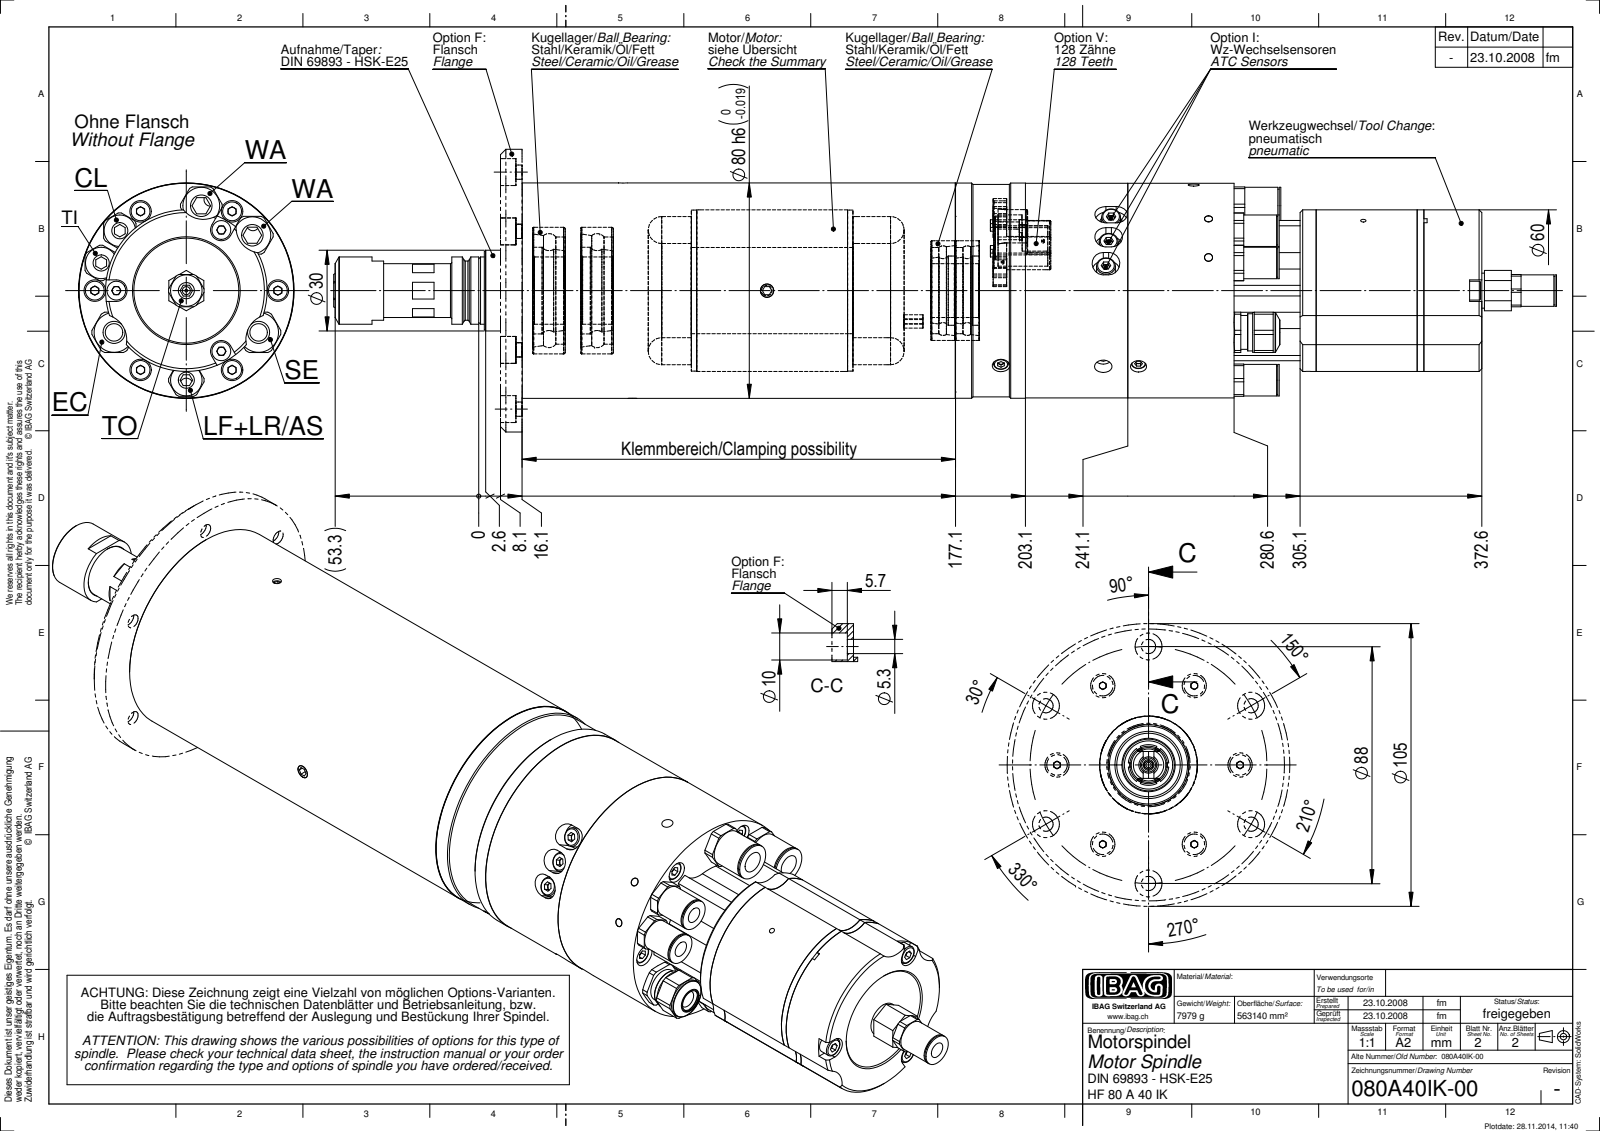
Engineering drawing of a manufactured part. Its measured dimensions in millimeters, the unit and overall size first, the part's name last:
Units: millimetres
Overall size (bounding box): 449.93 × 80 × 80
Round holes (diameter × count): ⌀8 ×8, ⌀6 ×5, ⌀6.5 ×3, ⌀3 ×2, ⌀8.2 ×2, ⌀3.4 ×1, ⌀4.2 ×1, ⌀20 ×1, ⌀30.2 ×1, ⌀36.3 ×1
Round bosses / shafts (diameter × count): ⌀7.64 ×6, ⌀7 ×6, ⌀11.7 ×4, ⌀14.8 ×2, ⌀13.79 ×2, ⌀13.7 ×2, ⌀12.59 ×2, ⌀80 ×1
Partial cylindrical surfaces — rounded edges, fillets, slot ends (radius × count): R9.5 ×12, R4.15 ×6, R6.6 ×4, R4 ×3, R7.75 ×2, R8.25 ×2, R22.4 ×1, R29 ×1
Main face-to-face distances: 169, 64, 134, 303, 70, 233, 195, 272.5, 103.5, 39.5
Hole centre spacings: 34, 17.07, 46.01, 58.89, 62.79, 33.25, 10.54, 17.42
Bodies: 0 solids, 689 faces (315 planar, 247 cylindrical, 127 other)
Part name (STEP PRODUCT): 080A40IK-00
STEP written by: SolidWorks 2009 (CONFIG_CONTROL_DESIGN)
